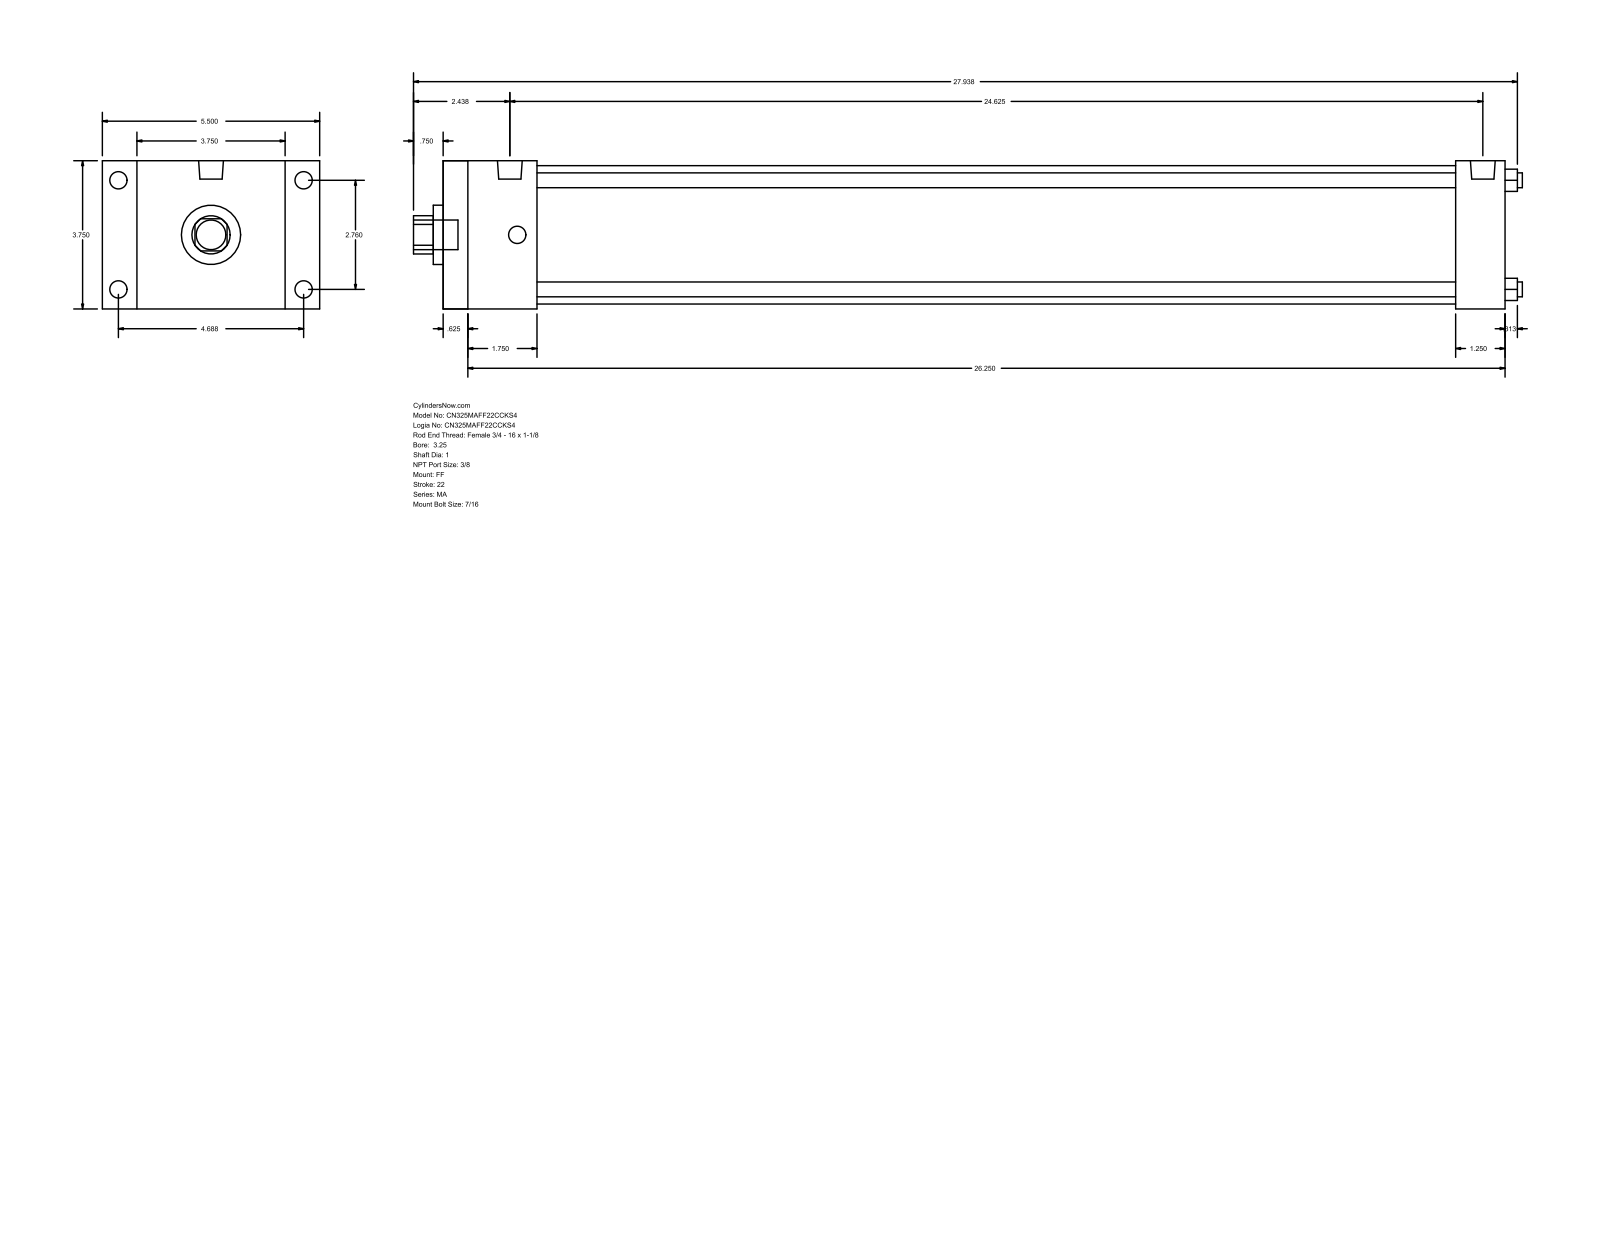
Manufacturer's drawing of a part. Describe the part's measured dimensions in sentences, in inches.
The part is named "MA_FF__0325_1". Its 3-D file was written by "GSSL Pune (CONFIG_CONTROL_DESIGN)". It is 0 solids with 92 faces: 64 planar, 28 cylindrical and 0 other. Overall it measures 28.063 by 5.5 by 3.75 inches. Round holes: 4 of diameter 0.375, 1 of diameter 1, 1 of diameter 1.5, 1 of diameter 3.5. Round bosses or shafts: 8 of diameter 0.437, 2 of diameter 0.627, 1 of diameter 0.75. Partial cylindrical surfaces (rounded edges, fillets, slot ends): 1 of radius 0.484. The main face-to-face distances are 3.75, 26.875, 0.625, 26.25, 0.875, 4.625, 2.375, 25.625, 1.75, 25. The hole center spacings are 1.952, 2.76, 3.903.
